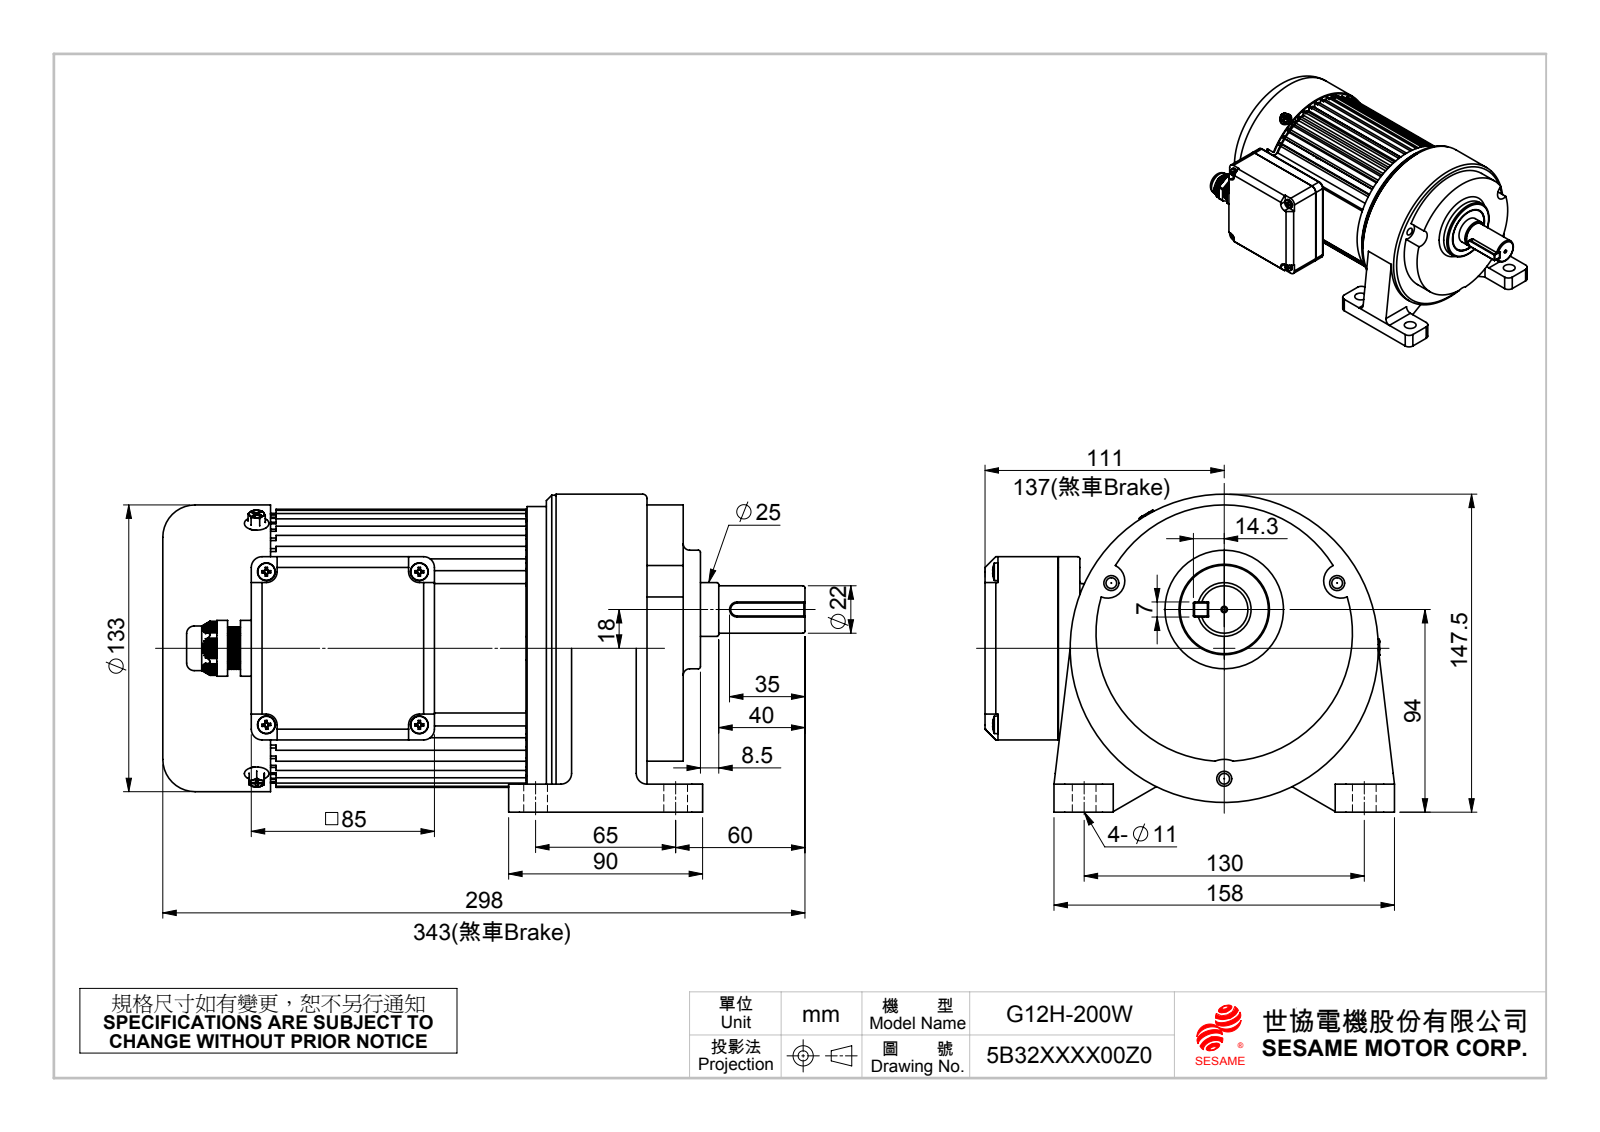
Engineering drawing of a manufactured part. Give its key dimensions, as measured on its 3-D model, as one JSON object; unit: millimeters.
{"part_name": "(標準品)G12H200W(5B32XXX100)(減速比共用); 出線盒下蓋; 成品-塑膠T盒; 外六角內十字螺絲M5 x 10_ISO 4162 - M5 x 10 x 10-N (+8 more)", "step_written_by": "SolidWorks 2010 (CONFIG_CONTROL_DESIGN)", "units": "millimeters", "bodies": {"solids": 19, "faces": 2648, "planar": 797, "cylindrical": 840, "other": 1011}, "overall_size": [298, 190, 147.5], "volume_mm3": 3178000, "surface_area_mm2": 447549, "round_holes": [[5, 14], [3.3, 9], [8, 4], [11, 4], [4.2, 3], [7, 3], [2, 1], [7.5, 1], [10.8, 1], [16.5, 1], [24.95, 1], [42, 1]], "round_bosses_or_shafts": [[8.3, 4], [4, 4], [5, 3], [143, 1], [142, 1], [133, 1], [131.5, 1], [131, 1]], "partial_cylinders_radius": [[1, 74], [5, 18], [1.03, 8], [2.75, 6], [2, 4], [2.55, 4], [3.55, 4], [8, 2]], "face_to_face_distances": [2, 10, 138.95, 13, 148.95, 110, 18, 3, 11.05, 135.95], "hole_center_spacings": [45, 71, 60.5, 11, 11.5, 14.6, 14.79, 17.36]}
